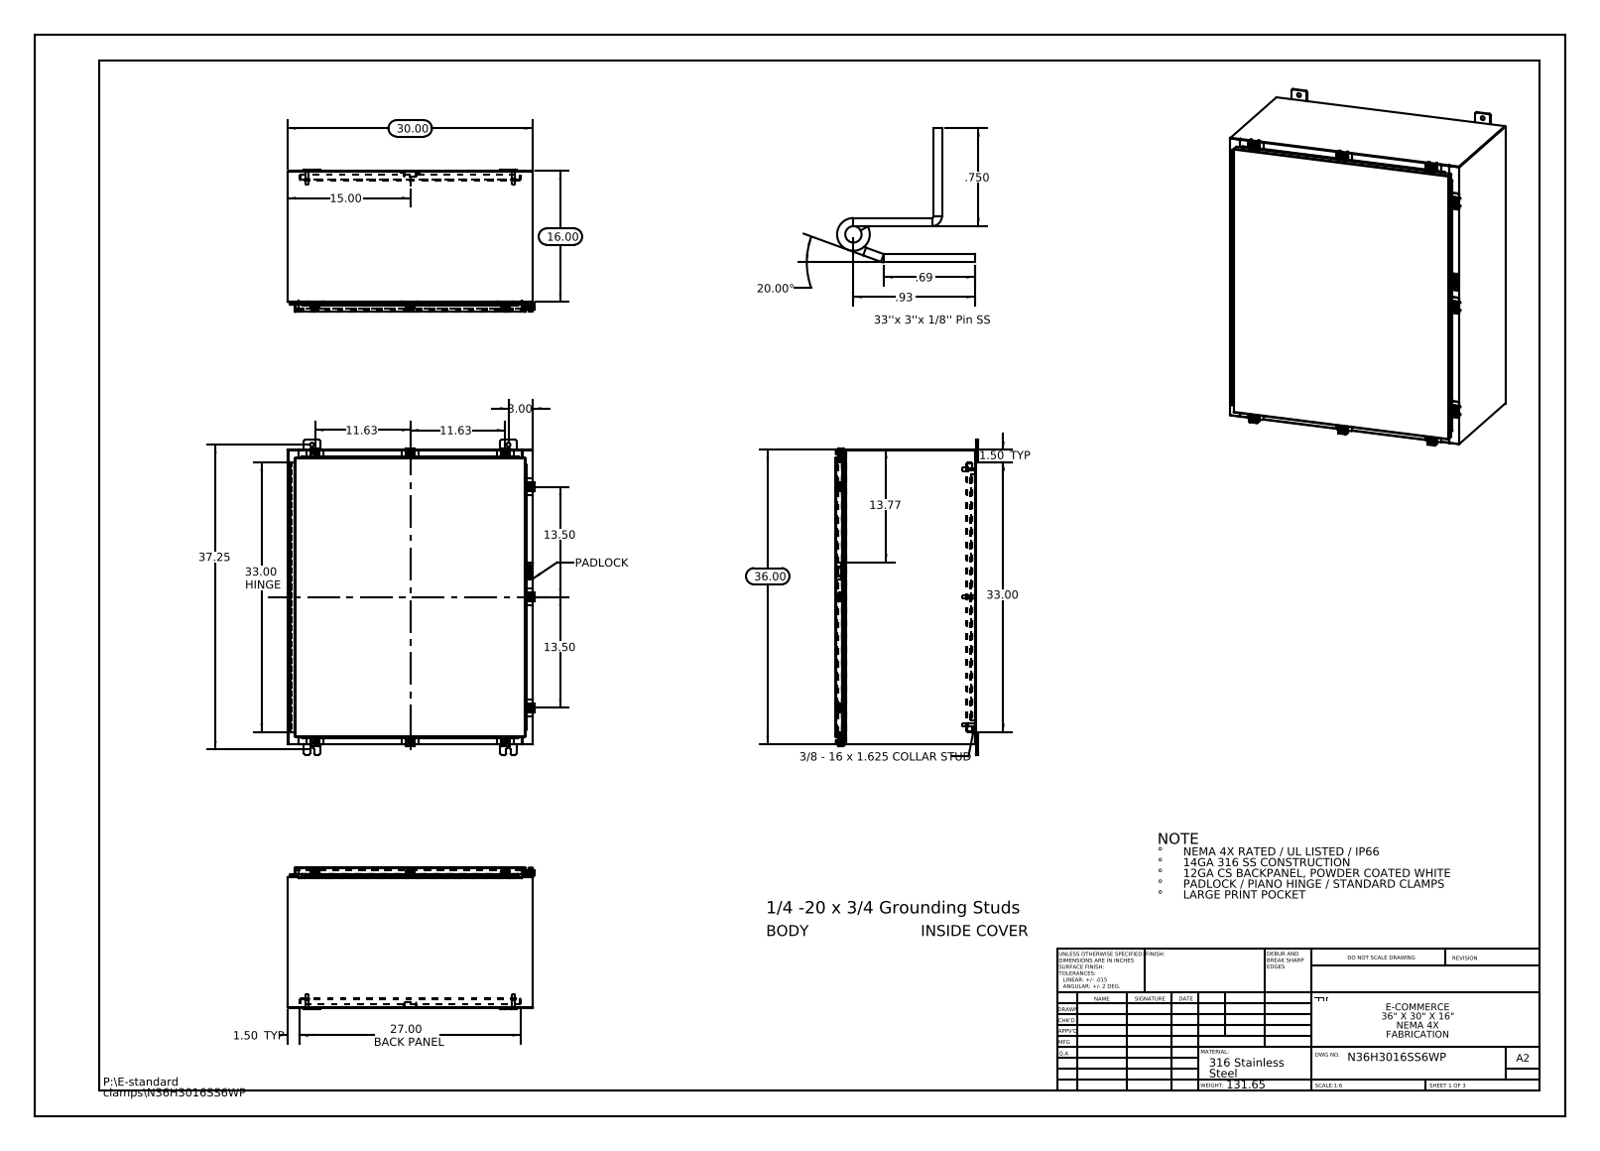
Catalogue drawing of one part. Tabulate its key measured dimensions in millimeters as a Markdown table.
| quantity | value |
| --- | --- |
| part name | N36H3016SS6WP 22101002; N36H3016SS6WP 22104005_DEFAULT; N36H3016SS6WP Clamp Bracket; N36H3016SS6WP Mounting Feet (+8 more) |
| STEP written by | SolidWorks 2013 (CONFIG_CONTROL_DESIGN) |
| units | millimeters |
| bodies | 65 solids, 2456 faces (1288 planar, 1028 cylindrical, 140 other) |
| overall size | 977.9 × 767.4 × 441.7 |
| volume | 7 554 000 mm³ |
| surface area | 7 501 000 mm² |
| round holes (diameter × count) | 12.7 × 10, 5.4 × 9, 6.6 × 9, 3.2 × 2, 3.2 × 1 |
| round bosses / shafts (diameter × count) | 6.4 × 10, 12.7 × 9, 10.1 × 9, 15.9 × 6, 9.5 × 6, 8.4 × 6 |
| partial cylindrical surfaces (radius × count) | 1.5 × 42, 0.3 × 31, 2.2 × 25, 4.8 × 24, 3 × 18, 3.6 × 18, 1.3 × 13, 2 × 12 |
| main face-to-face distances | 1.9, 435, 760.1, 433.1, 436.9, 2.6, 912.5, 25.4, 409.6, 27.3 |
| hole center spacings | 396.9, 451, 754.2, 847.5, 947.6, 641.4, 900.5, 47.2 |
